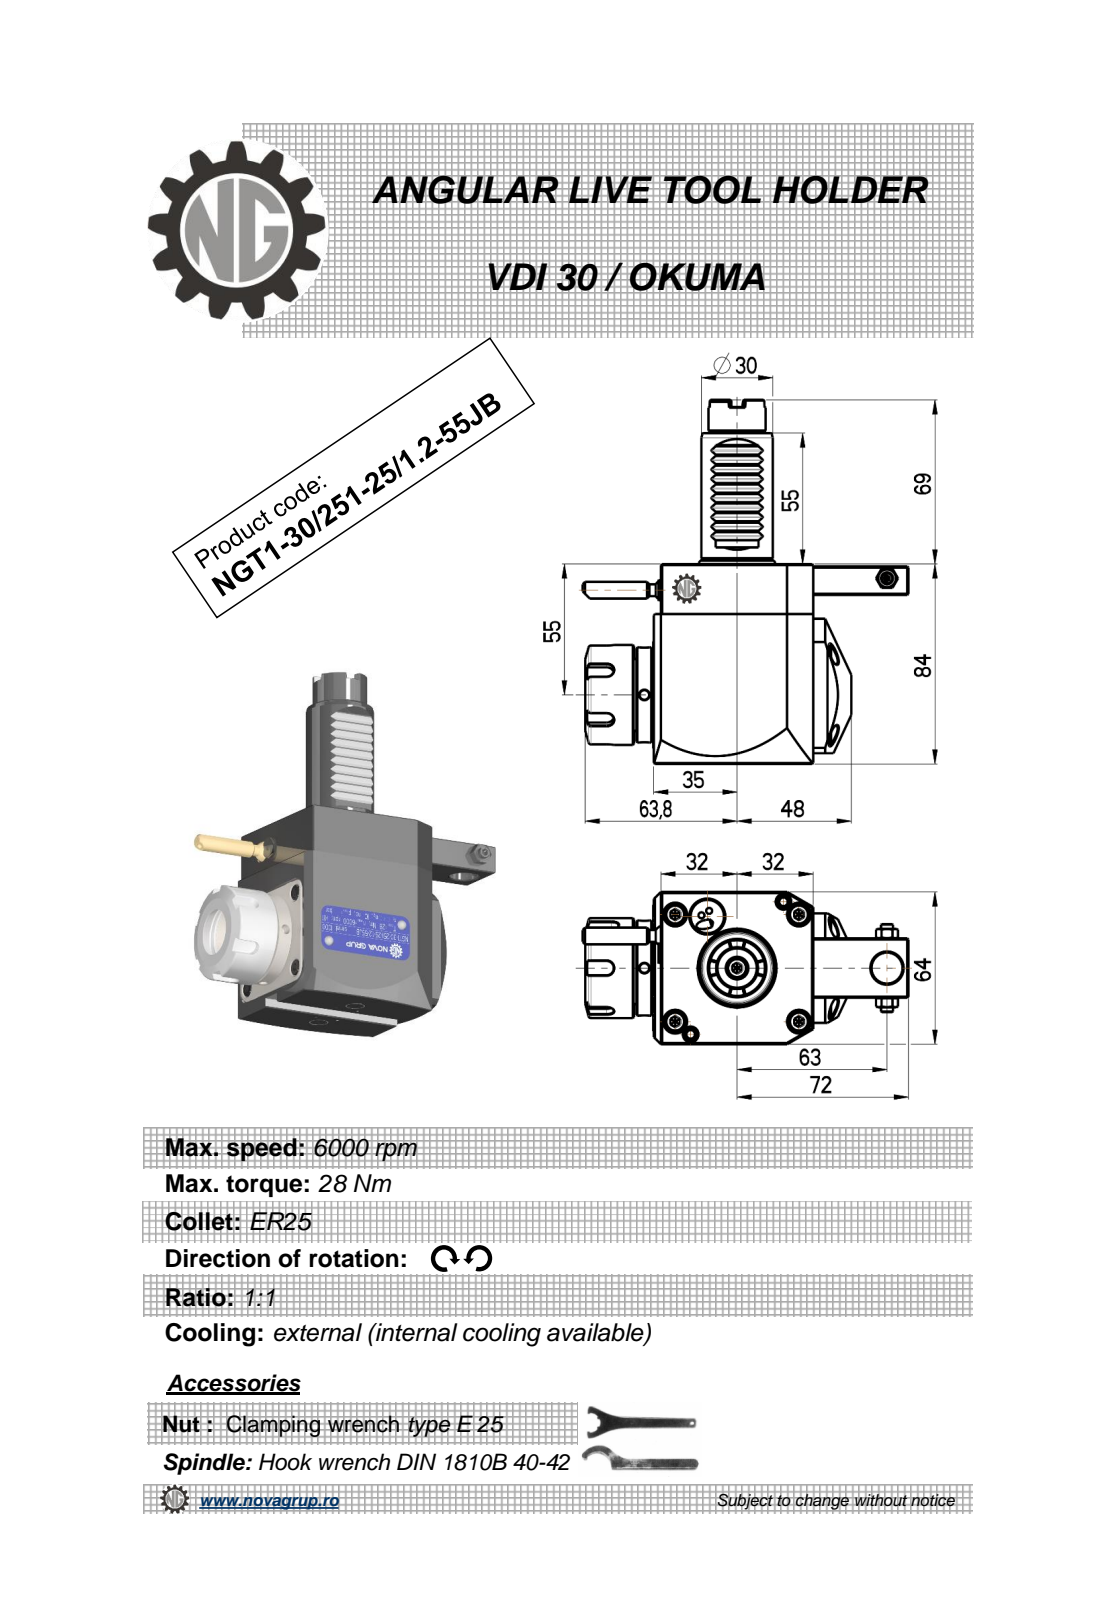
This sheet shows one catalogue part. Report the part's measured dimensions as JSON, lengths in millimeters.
{"part_name": "NGT1_30_251_25_1_2_55JB", "step_written_by": "PRO/ENGINEER BY PARAMETRIC TECHNOLOGY CORPORATION, 2010280 (CONFIG_CONTROL_DESIGN)", "units": "millimeters", "bodies": {"solids": 1, "faces": 477, "planar": 209, "cylindrical": 90, "other": 178}, "overall_size": [153, 136.88, 65.6], "volume_mm3": 459054, "surface_area_mm2": 49304, "round_holes": [[4, 2], [2.5, 1], [3, 1], [4.2, 1], [9.5, 1], [13, 1], [17, 1], [20.3, 1]], "round_bosses_or_shafts": [[8.96, 2], [5, 2], [42, 1], [40, 1], [33, 1], [30, 1], [24, 1], [7, 1]], "partial_cylinders_radius": [[0.26, 12], [0.3, 10], [3, 5], [3.5, 4], [160, 2], [32, 1]], "face_to_face_distances": [64, 84, 67, 67.2, 3, 3.2, 83, 1, 0.5, 80], "hole_center_spacings": [14.08, 38.95, 46.02, 48, 63, 101.95, 113.11]}
